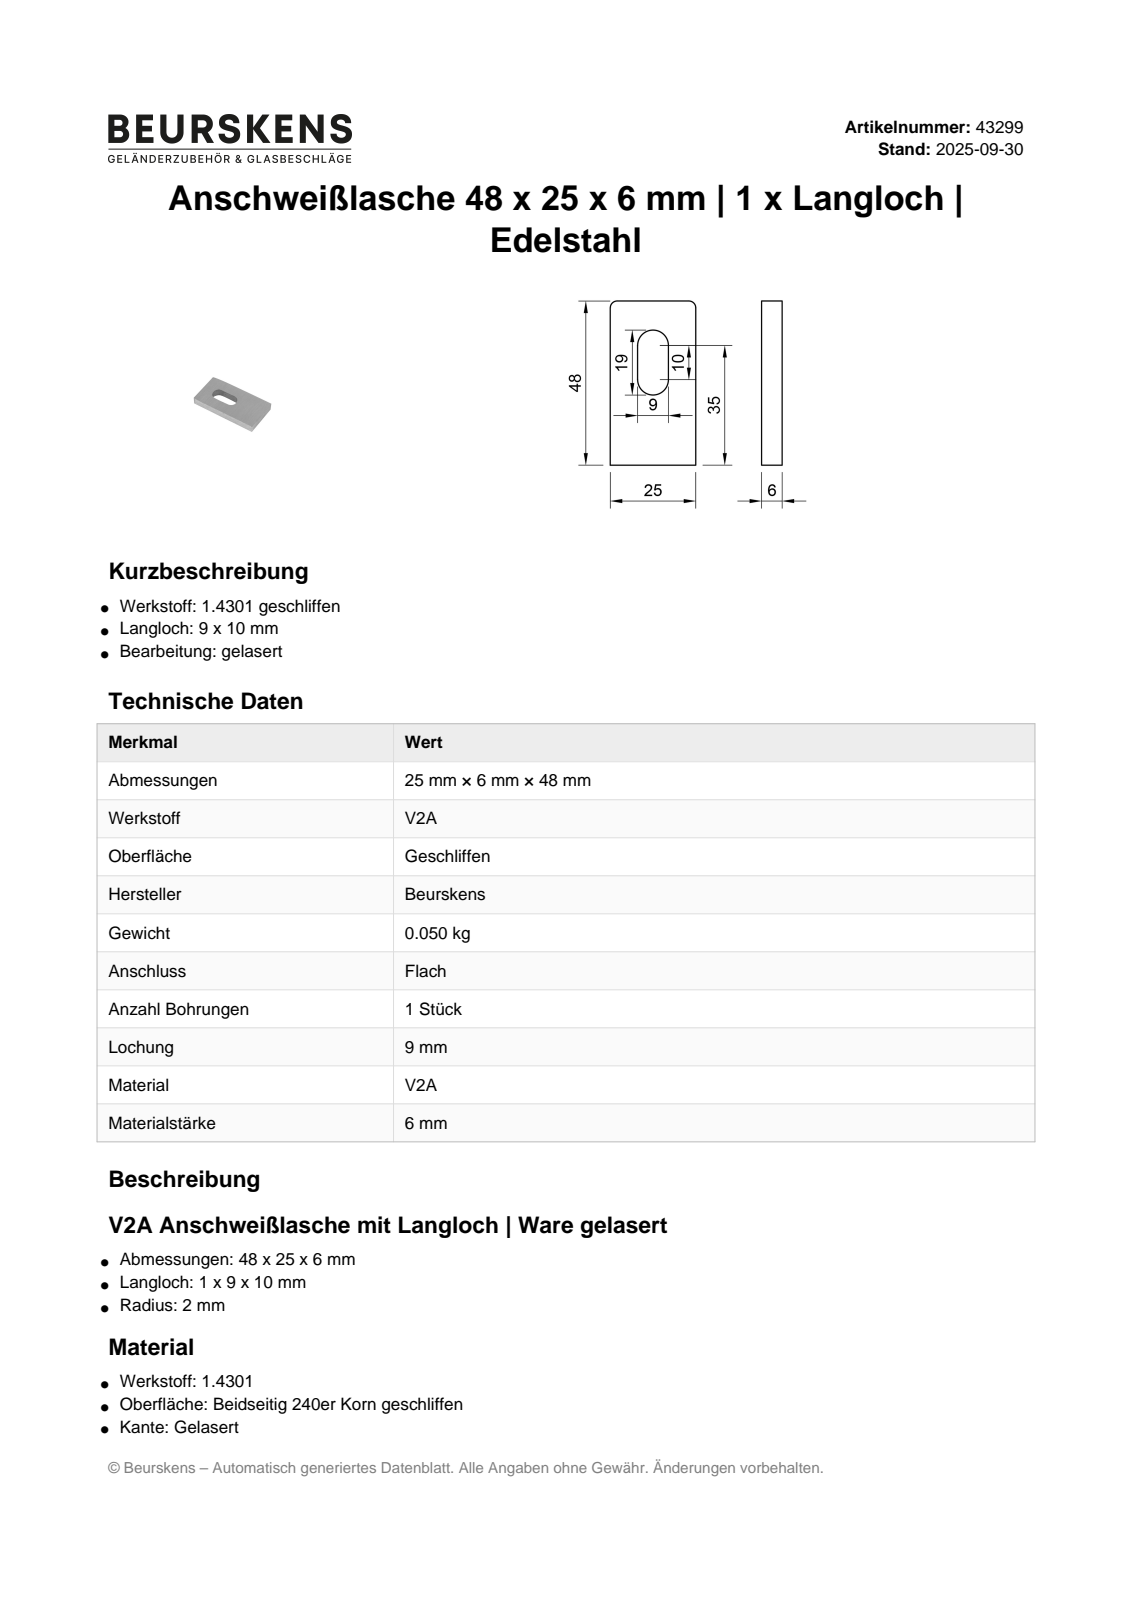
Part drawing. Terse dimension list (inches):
name: 43299
written by: Autodesk Inventor 2022 (AUTOMOTIVE_DESIGN)
unit: in
bodies: 1 solid, 12 faces (8 planar, 4 cylindrical, 0 other)
size: 1.89 × 0.984 × 0.236
volume: 0.382 in³; area: 5.03 in²
rounds: 2× R0.079, 2× R0.177
face distances: 0.236, 0.984, 1.89, 0.315, 0.669, 0.354
